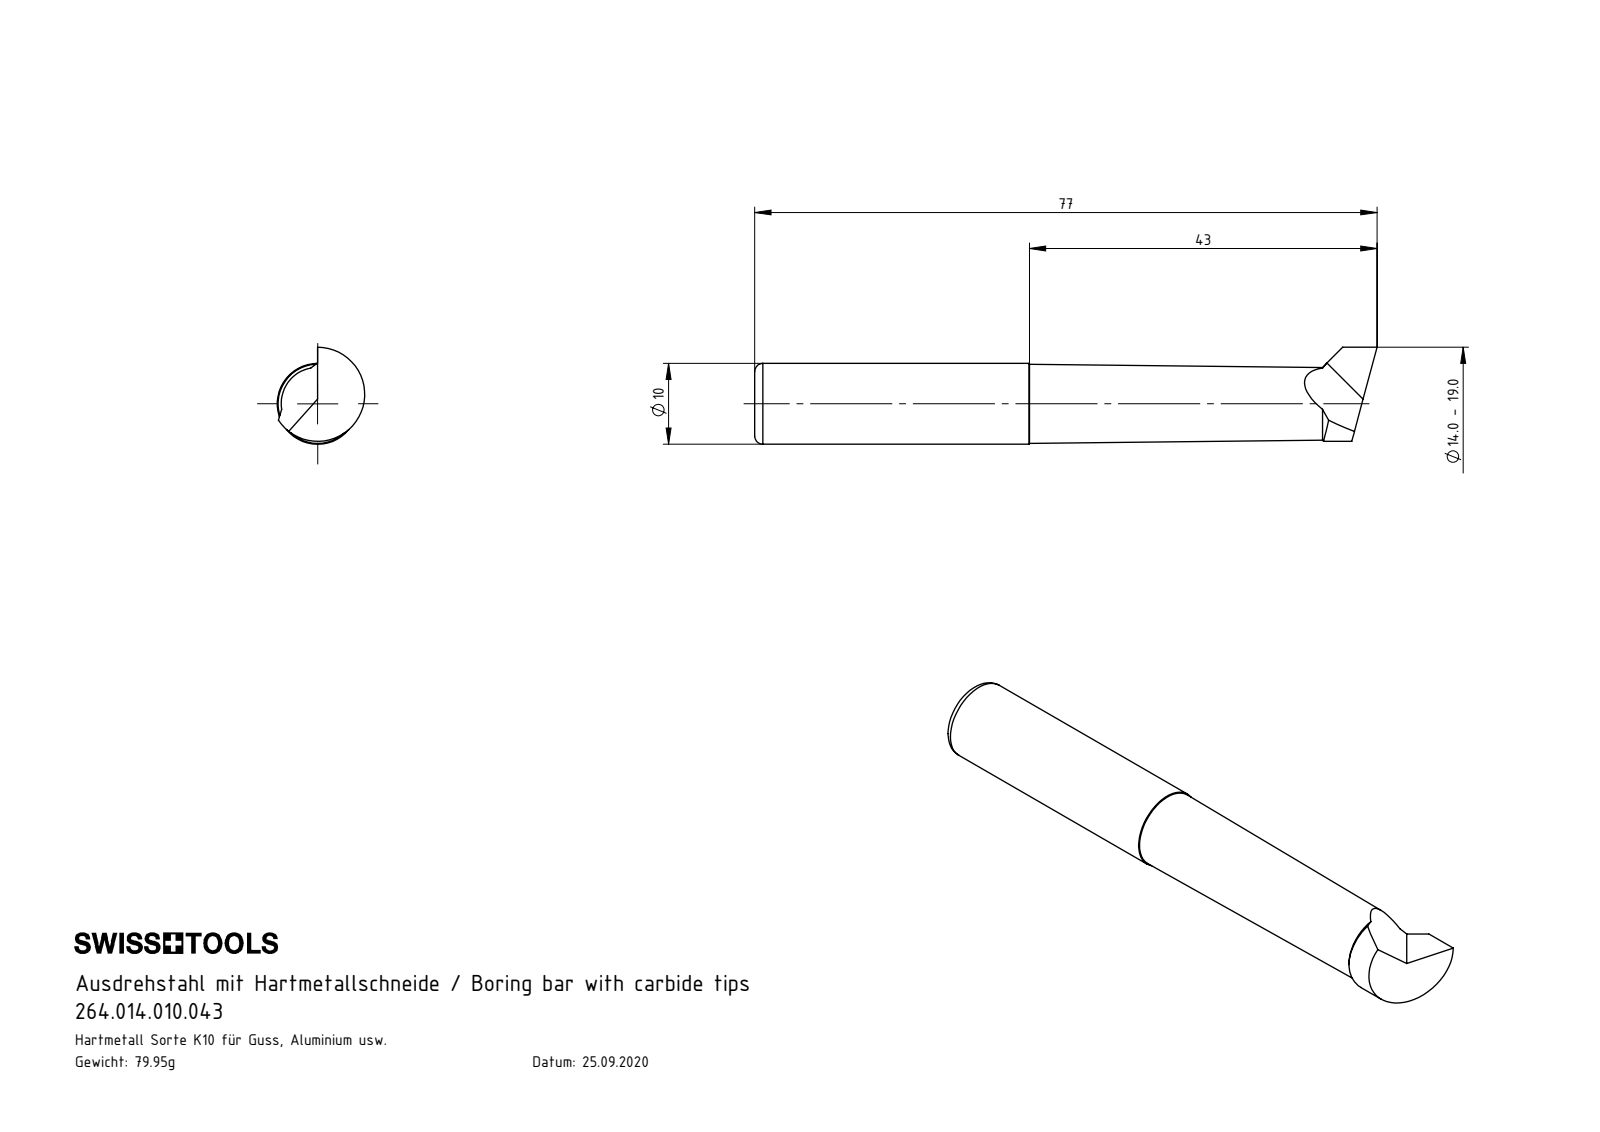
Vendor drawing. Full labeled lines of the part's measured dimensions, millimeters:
Part name (STEP PRODUCT): 264.014.010.043
STEP written by: SolidWorks 2022 (CONFIG_CONTROL_DESIGN)
Units: millimetres
Bodies: 1 solid, 16 faces (4 planar, 3 cylindrical, 9 other)
Overall size (bounding box): 77 × 12 × 10.82
Volume: 5 514 mm³ · Surface area: 2 452 mm²
Round bosses / shafts (diameter × count): ⌀10 ×1
Partial cylindrical surfaces — rounded edges, fillets, slot ends (radius × count): R5.82 ×1
